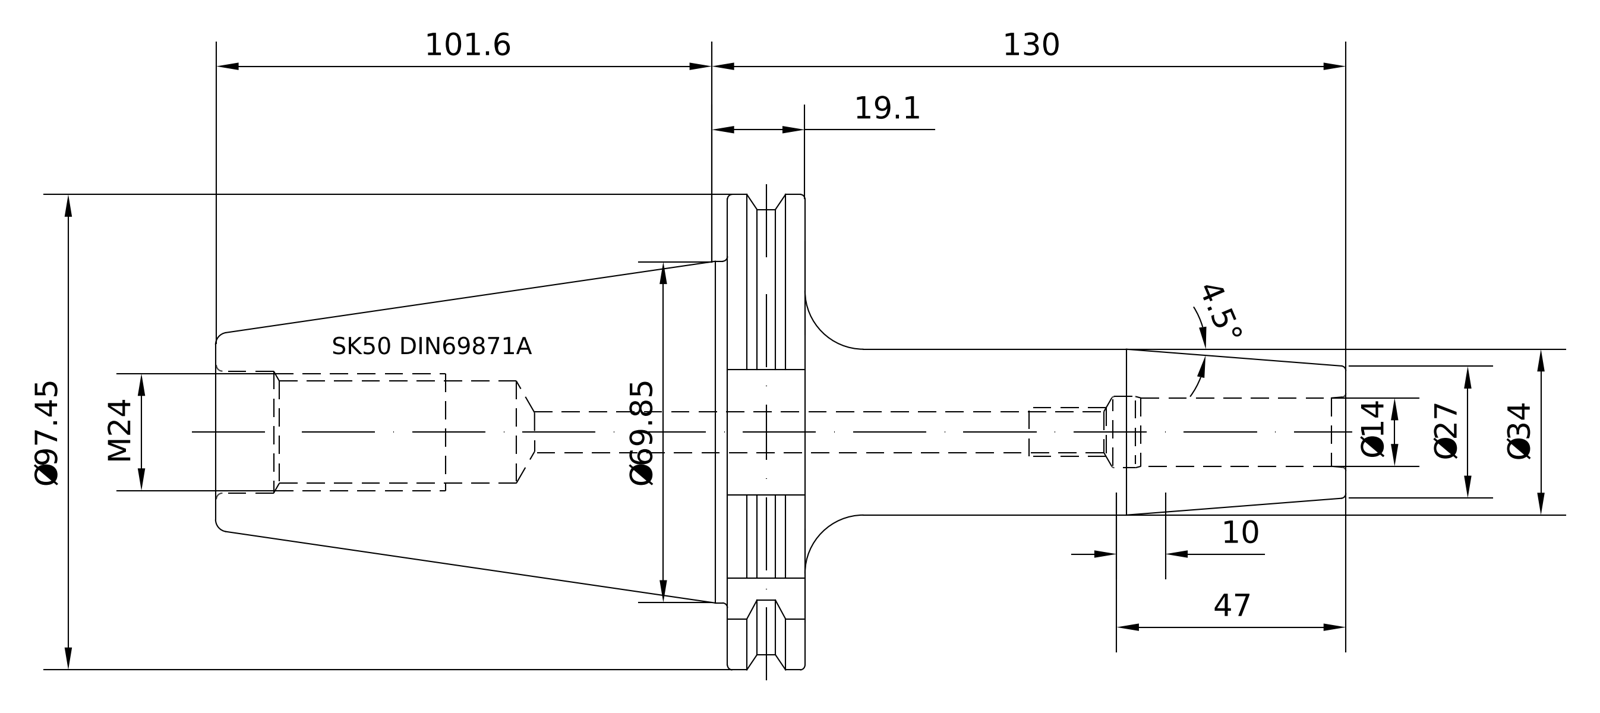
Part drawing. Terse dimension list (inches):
name: 50-444-14
written by: PRO/ENGINEER BY PARAMETRIC TECHNOLOGY CORPORATION, 2010430 (CONFIG_CONTROL_DESIGN)
unit: in
bodies: 1 solid, 93 faces (21 planar, 24 cylindrical, 48 other)
size: 9.118 × 3.837 × 3.701
volume: 26.17 in³; area: 85.61 in²
holes: 1× ⌀0.551, 1× ⌀0.817, 1× ⌀0.985, 1× ⌀1.012
bosses: 1× ⌀3.583, 1× ⌀2.722, 1× ⌀1.339, 1× ⌀0.945
rounds: 1× R0.069, 1× R1.919
face distances: 0.624, 2.866, 4.126, 4.75, 9.118, 4.992, 4.368, 1.016, 7.268, 3.142
